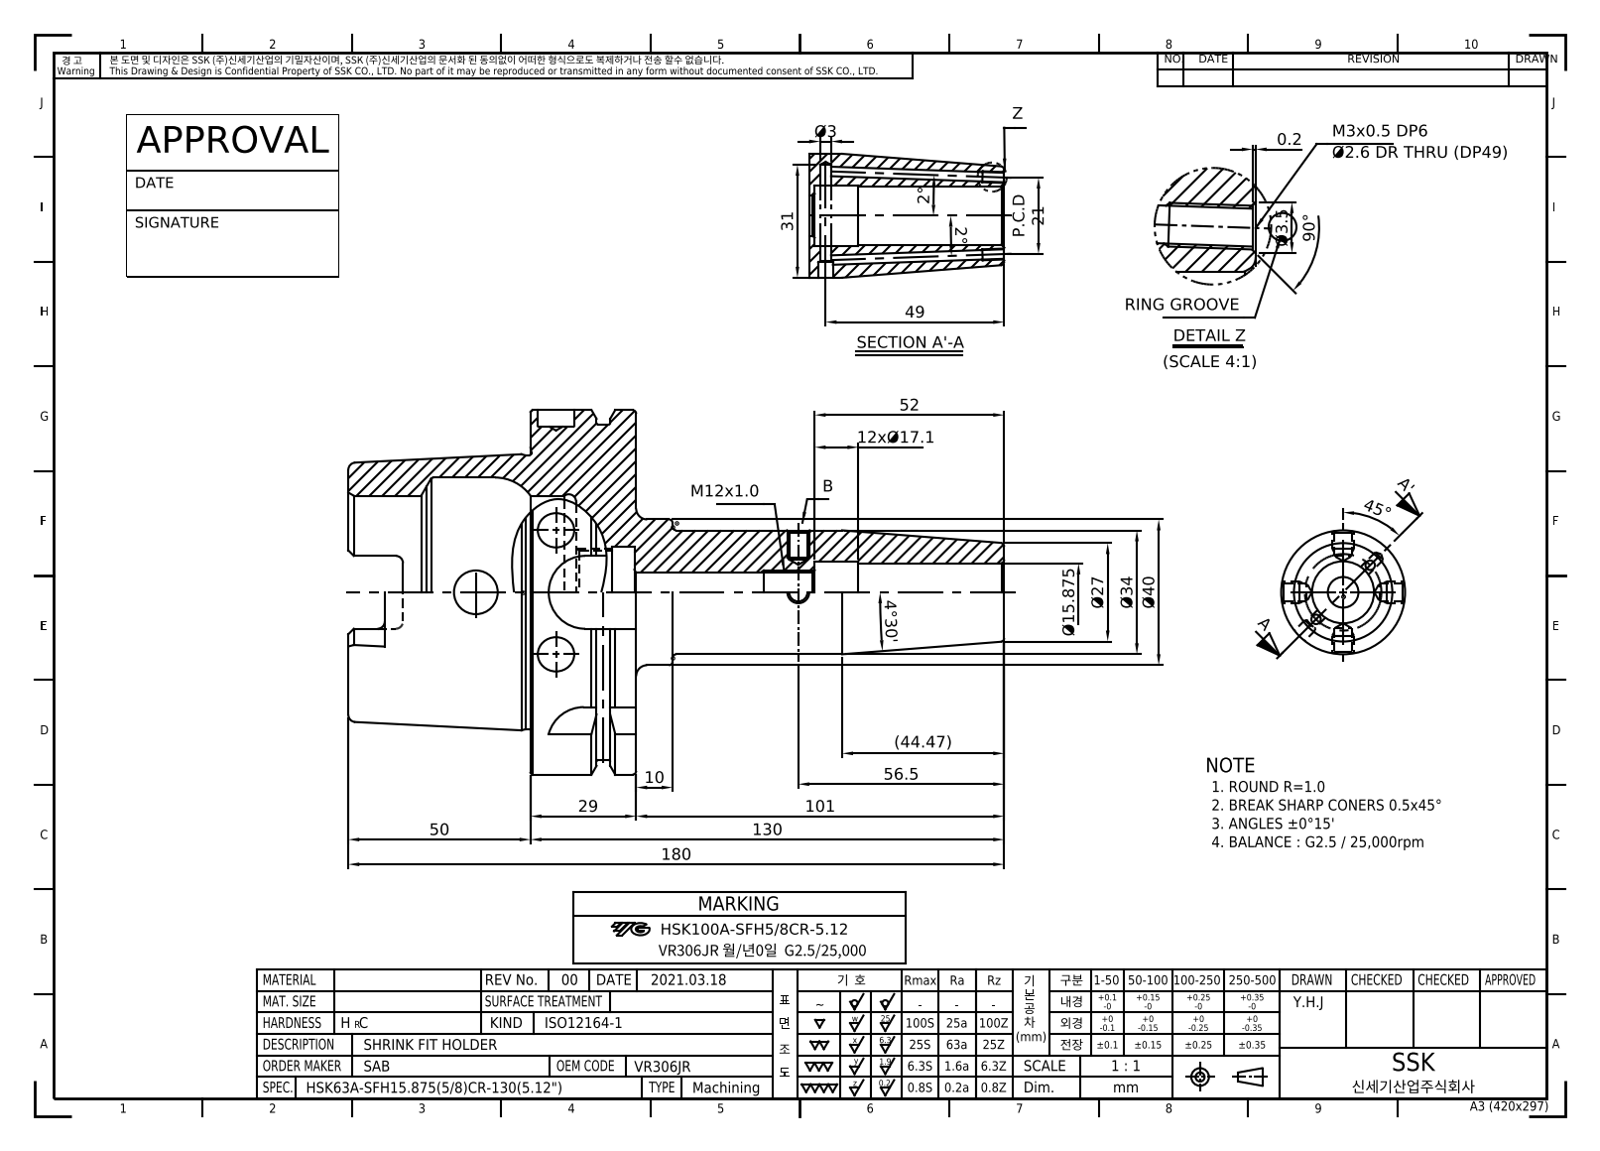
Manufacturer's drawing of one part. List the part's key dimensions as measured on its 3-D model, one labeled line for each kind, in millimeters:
Part name (STEP PRODUCT): LO-HSK100A-SFH15.875CR-130
STEP written by: Autodesk Inventor 2022 (AUTOMOTIVE_DESIGN)
Units: millimetres
Bodies: 1 solid, 120 faces (38 planar, 37 cylindrical, 45 other)
Overall size (bounding box): 180 × 100 × 100
Volume: 326 012 mm³ · Surface area: 64 480 mm²
Round holes (diameter × count): ⌀2.46 ×2, ⌀10 ×1, ⌀10.92 ×1, ⌀12 ×1, ⌀15.87 ×1, ⌀17.07 ×1, ⌀22.38 ×1, ⌀25 ×1, ⌀53 ×1, ⌀63 ×1
Round bosses / shafts (diameter × count): ⌀100 ×1, ⌀92 ×1, ⌀75.41 ×1, ⌀40 ×1, ⌀34 ×1
Partial cylindrical surfaces — rounded edges, fillets, slot ends (radius × count): R2 ×6, R4.88 ×4, R10 ×4
Main face-to-face distances: 29, 12.5, 16.5, 62.5, 50, 79, 88, 78.5, 28.5, 16
